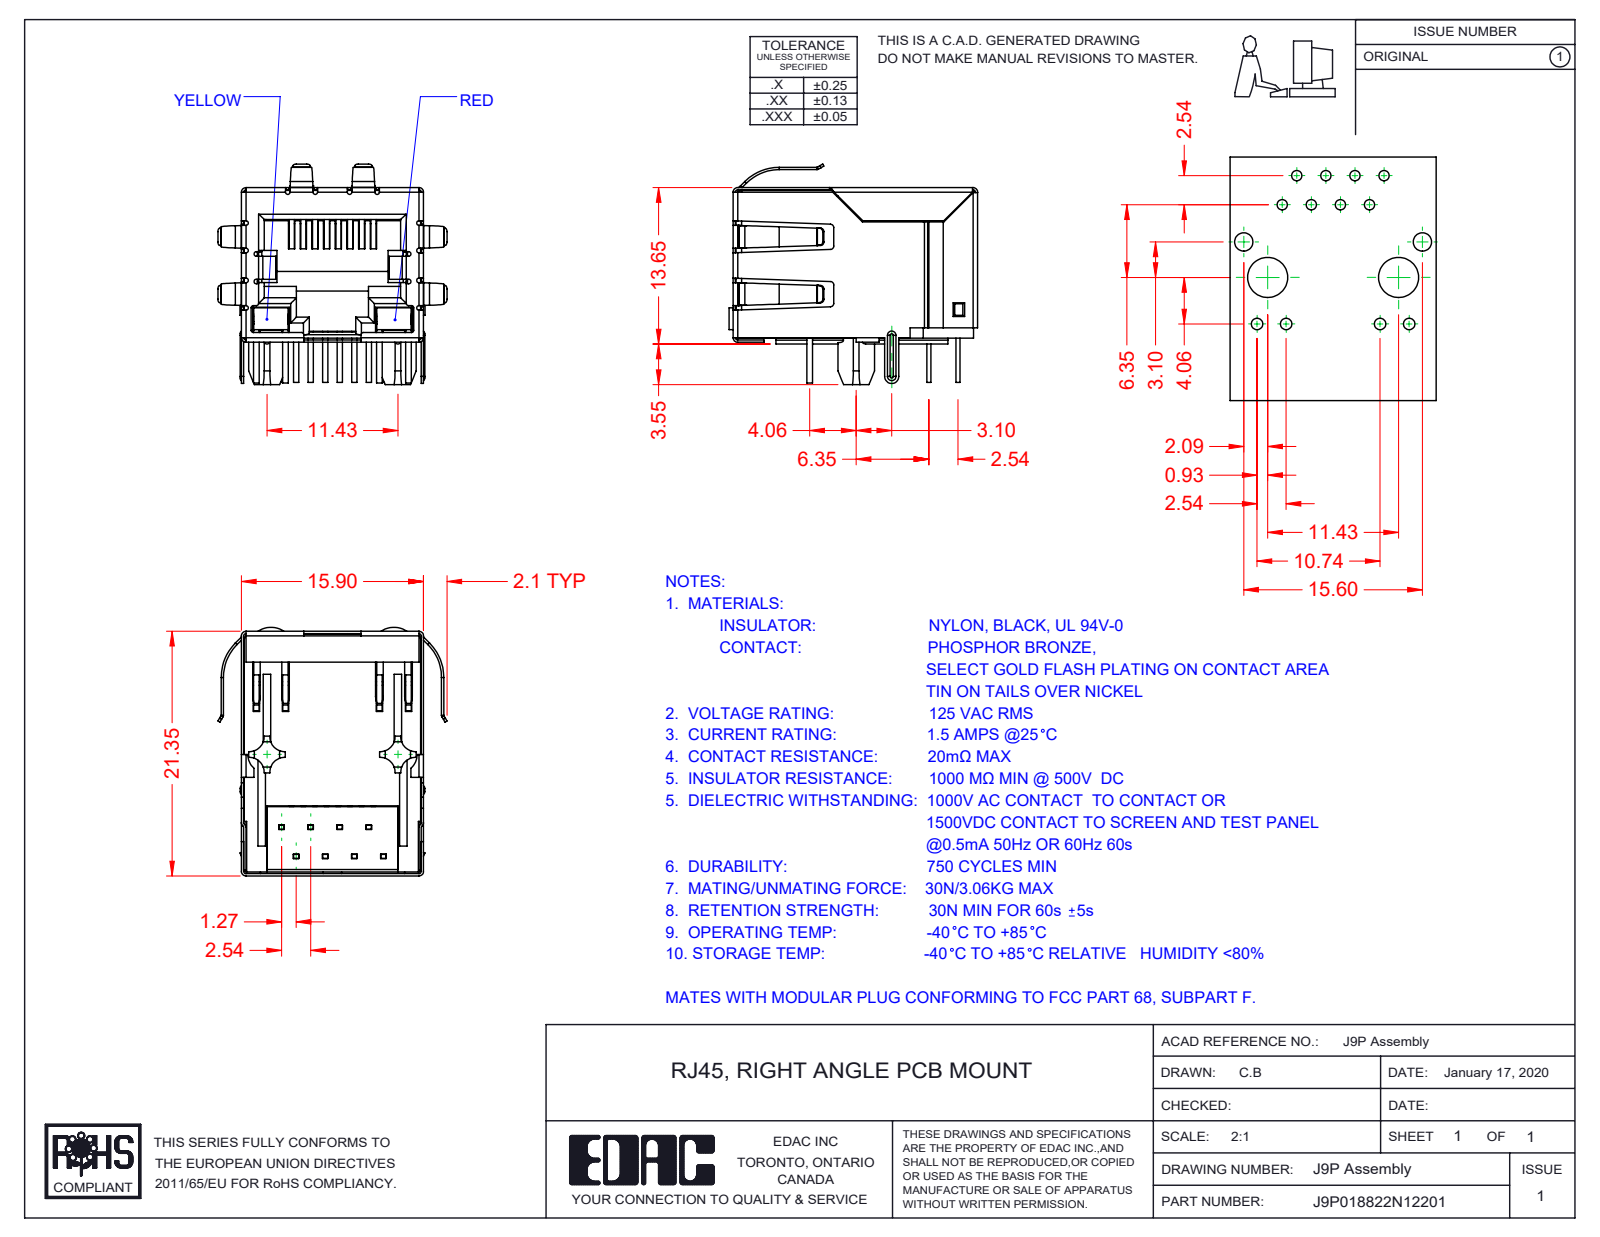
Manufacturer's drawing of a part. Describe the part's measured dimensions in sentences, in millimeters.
The part is named "9P-LED Assembly; 9P-LED Contacts; 9P-LED Insulator; J9P018822N12202 (+4 more)". Its 3-D file was written by "SolidWorks 2016 (CONFIG_CONTROL_DESIGN)". It is 13 solids with 1472 faces: 1042 planar, 336 cylindrical and 94 other. Overall it measures 21.7 by 20 by 19.25 millimeters. Its volume is 2 687 cubic millimeters and its surface area 7 515 square millimeters. Partial cylindrical surfaces (rounded edges, fillets, slot ends): 39 of radius 0.2, 22 of radius 0.5, 20 of radius 0.3, 16 of radius 0.4, 8 of radius 1.3, 5 of radius 0.23, 4 of radius 0.11, 4 of radius 0.31. The main face-to-face distances are 15.45, 15.7, 15.65, 0.35, 0.54, 15.5, 12.36, 0.6, 1.4, 0.59.
